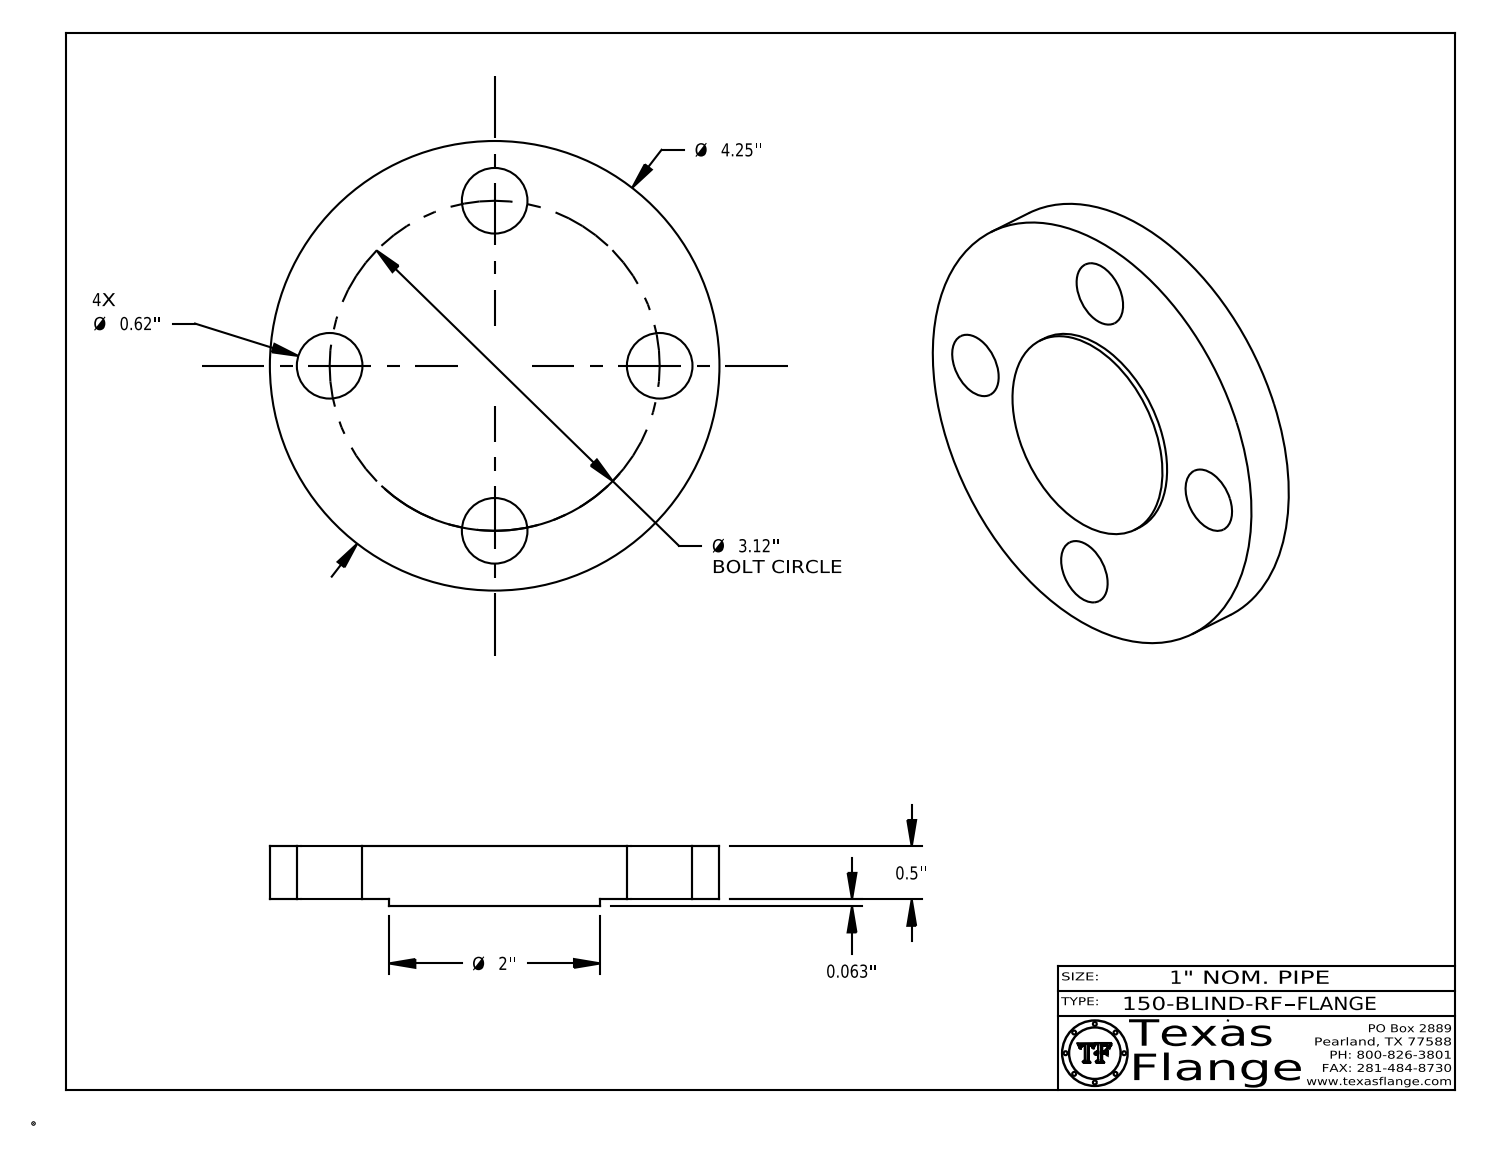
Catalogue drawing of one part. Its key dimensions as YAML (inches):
part_name: "150-BLIND-RF"
step_written_by: "CATIA V5 STEP AP214 (AUTOMOTIVE_DESIGN)"
units: inches
bodies: {solids: 1, faces: 400, planar: 368, cylindrical: 32, other: 0}
overall_size: [4.25, 4.25, 0.563]
volume: 6.684
surface_area: 37.01
round_holes:
  - {diameter: 0.62, count: 4}
  - {diameter: 0.495, count: 1}
round_bosses_or_shafts:
  - {diameter: 0.03, count: 8}
  - {diameter: 4.25, count: 1}
  - {diameter: 2, count: 1}
  - {diameter: 0.39, count: 1}
face_to_face_distances: [0.5, 0.063, 0.563, 0.548, 0.485, 0.015, 0.148, 0.144, 0.027, 0.122]
hole_center_spacings: [2.206, 1.194, 2.882, 3.12]
